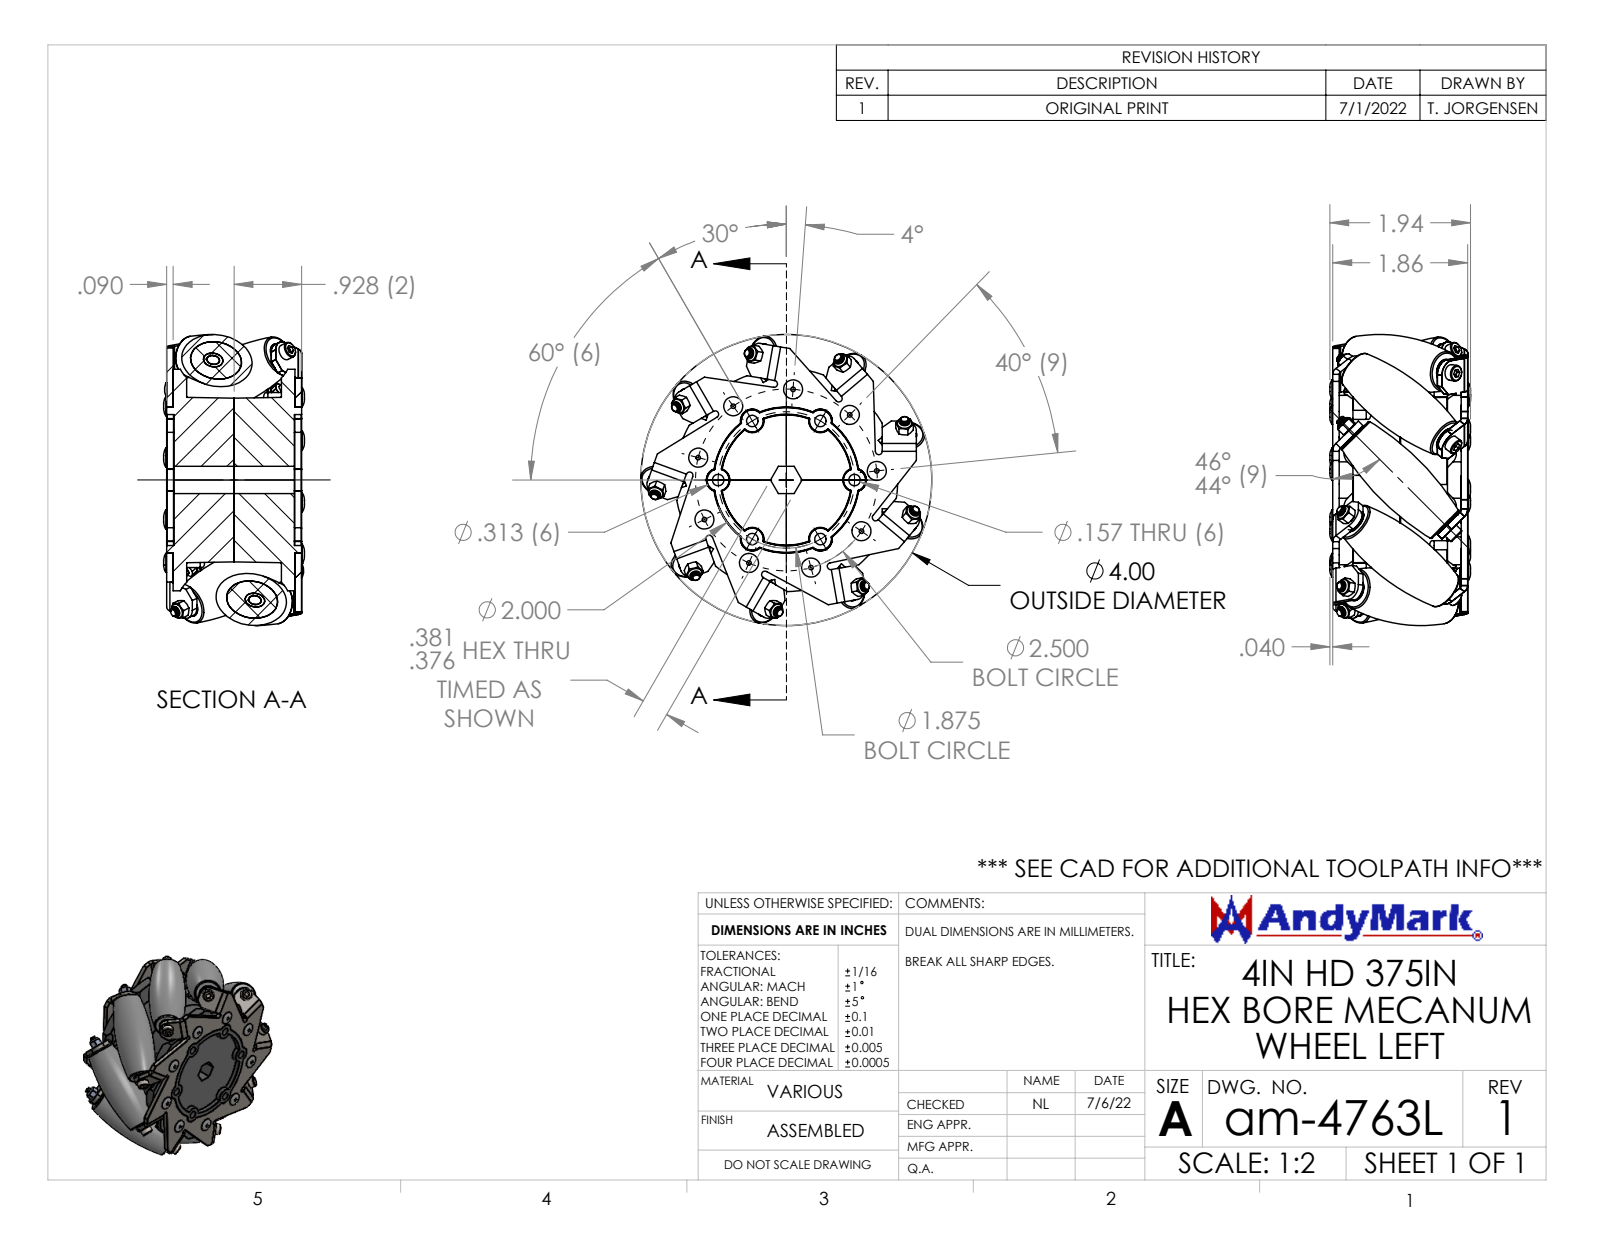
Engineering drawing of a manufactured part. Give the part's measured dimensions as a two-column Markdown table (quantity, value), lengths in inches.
| quantity | value |
| --- | --- |
| part name | am-4763L 4 in HD Mecanum 375H Left; 4HD Mecanum Roller Core; ip-xxxx_half 4HD 375H Mecanum Hub; ip-3026L_plate 4 HD Left Mecanum Plate (+6 more) |
| STEP written by | SolidWorks 2022 (CONFIG_CONTROL_DESIGN) |
| units | inches |
| bodies | 68 solids, 4717 faces (835 planar, 1568 cylindrical, 2314 other) |
| overall size | 4 × 4 × 1.936 |
| volume | 12.53 in³ |
| surface area | 244.6 in² |
| round holes (diameter × count) | 0.135 × 50, 0.063 × 18, 0.135 × 10, 0.123 × 9, 0.125 × 9, 0.187 × 9, 0.157 × 6, 0.252 × 2 |
| round bosses / shafts (diameter × count) | 0.287 × 18, 0.262 × 18, 0.125 × 18, 0.217 × 9, 0.187 × 9, 0.118 × 9, 0.252 × 1 |
| partial cylindrical surfaces (radius × count) | 0.005 × 49, 0.219 × 36, 0.062 × 33, 0.047 × 18, 0.063 × 18, 0.187 × 14, 0.152 × 10, 0.153 × 8 |
| main face-to-face distances | 0.09, 1.676, 1.766, 0.09, 0.928, 1.766, 1.856, 0.187, 1.489, 0.1 |
| hole center spacings | 1.25, 0.855, 2.349, 1.607, 0.434, 1.915, 2.165, 0.434 |
